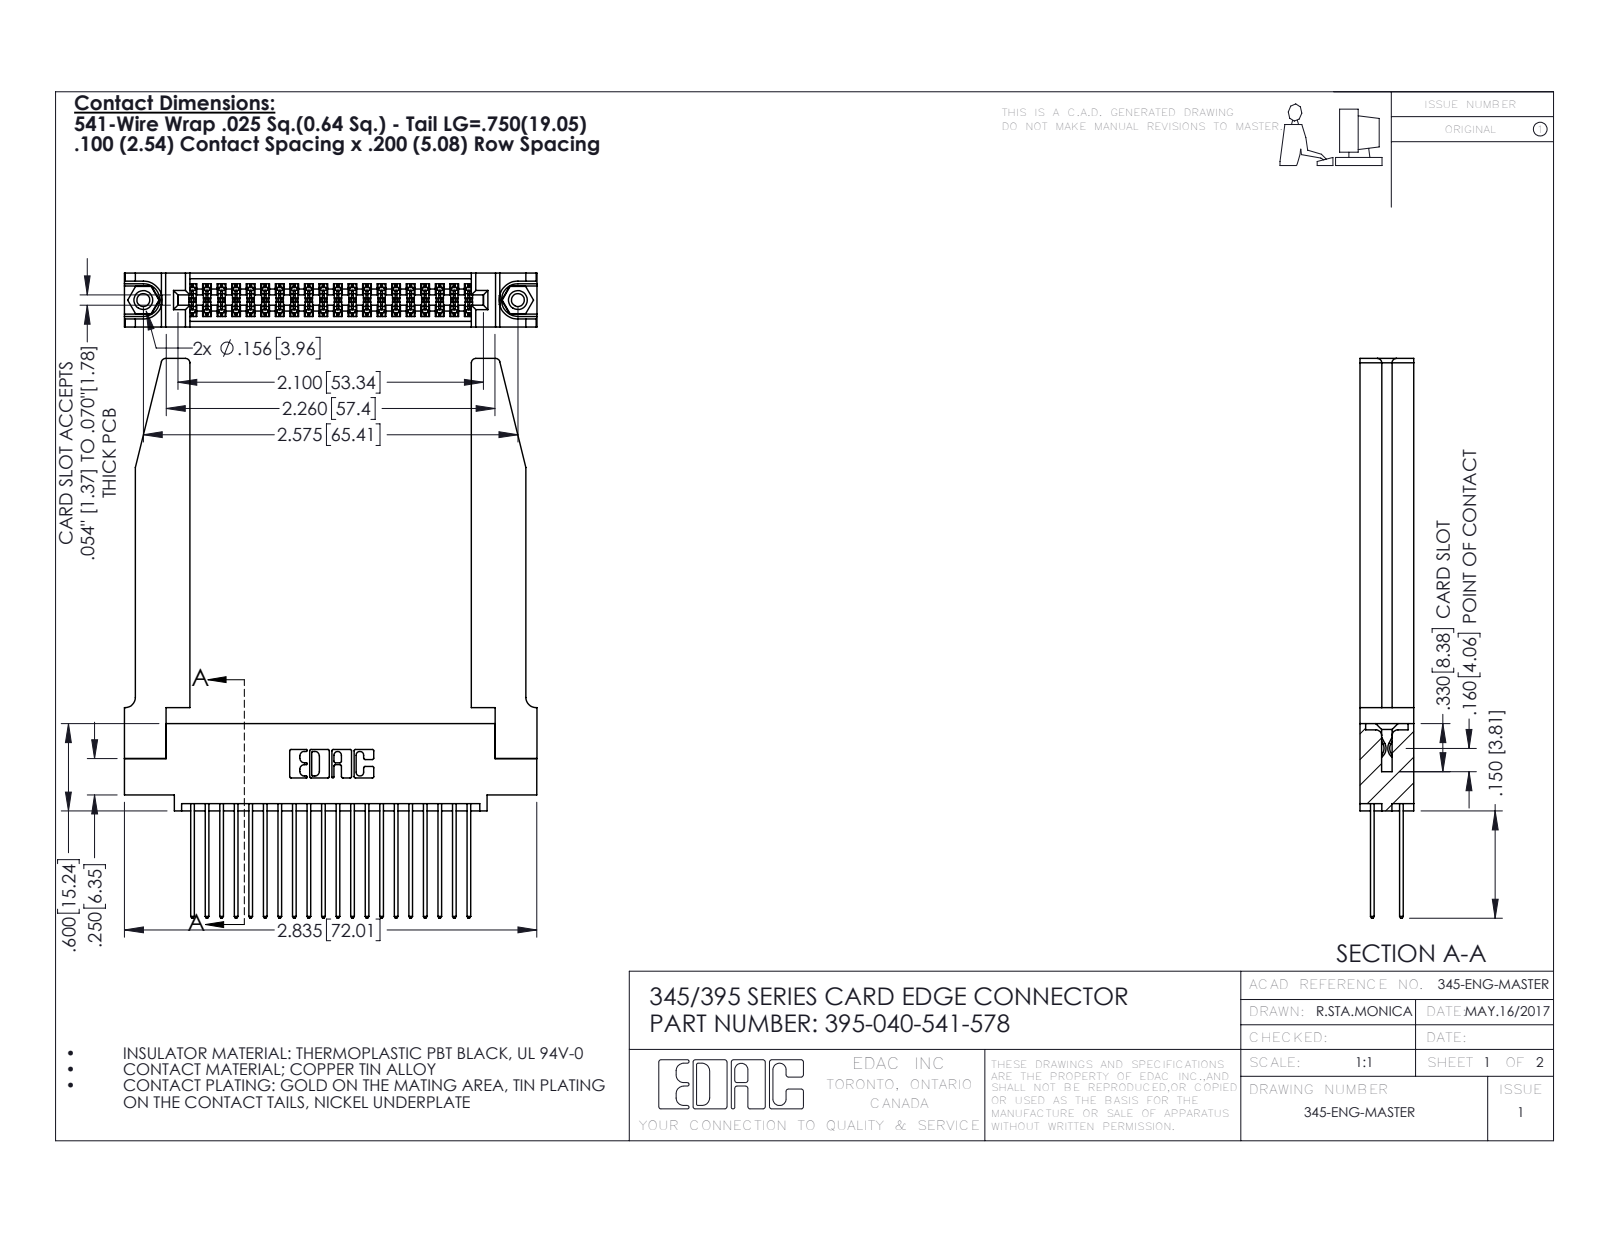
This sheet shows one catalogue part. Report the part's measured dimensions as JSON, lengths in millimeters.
{"part_name": "345-292-001_345-293-141; 395-040-541-578; 345-250-001_345-250-001-102; 345-220-078_345-220-078 (+1 more)", "step_written_by": "SolidWorks 2016 (CONFIG_CONTROL_DESIGN)", "units": "millimeters", "bodies": {"solids": 45, "faces": 2364, "planar": 1546, "cylindrical": 766, "other": 52}, "overall_size": [97.7, 72, 9.4], "volume_mm3": 14700, "surface_area_mm2": 17860, "round_holes": [[2.3, 2], [3.2, 2], [4, 2], [1.6, 1]], "round_bosses_or_shafts": [[3.9, 2]], "partial_cylinders_radius": [[0.2, 60], [0.3, 40], [0.3, 22], [0.8, 8], [0.2, 6], [0.8, 6], [0.7, 3], [0.4, 2]], "face_to_face_distances": [9.4, 1.8, 7.6, 5.1, 2.5, 6.9, 0.6, 5.7, 3.8, 3.8], "hole_center_spacings": [6.9, 59.5, 65.4]}
